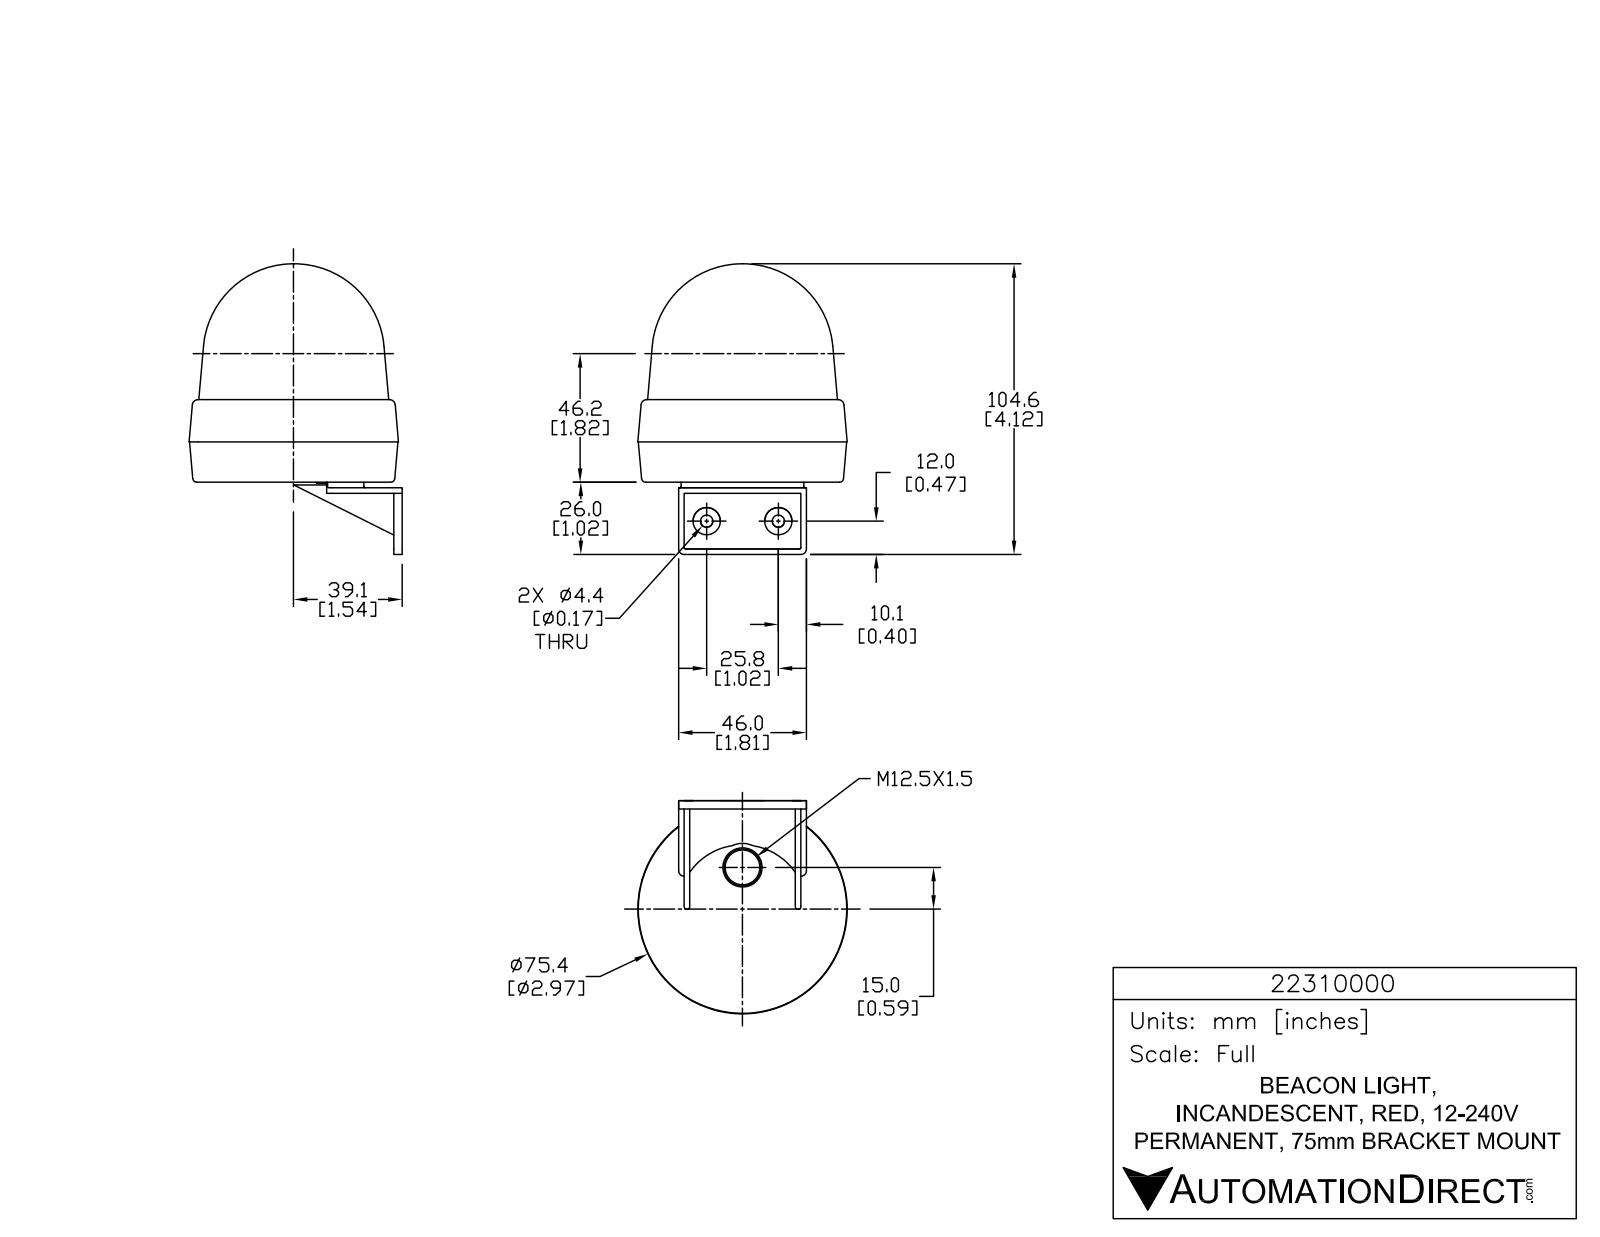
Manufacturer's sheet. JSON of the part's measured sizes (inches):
{"part_name": "22310000", "step_written_by": "SolidWorks 2015 (AUTOMOTIVE_DESIGN)", "units": "inches", "bodies": {"solids": 1, "faces": 819, "planar": 549, "cylindrical": 180, "other": 90}, "overall_size": [4.117, 3.253, 2.967], "volume_in3": 16.02, "surface_area_in2": 41.97, "round_holes": [[0.059, 3], [0.173, 2]], "round_bosses_or_shafts": [[0.339, 3], [0.084, 3], [0.386, 2]], "partial_cylinders_radius": [[0.005, 9], [0.005, 6], [0.012, 6], [0.012, 6], [0.012, 6], [0.02, 6], [0.196, 6], [0.079, 4]], "face_to_face_distances": [0.079, 0.157, 1.574, 0.039, 0.118, 1.653, 1.496, 0.079, 1.654, 1.732], "hole_center_spacings": [1.016]}
